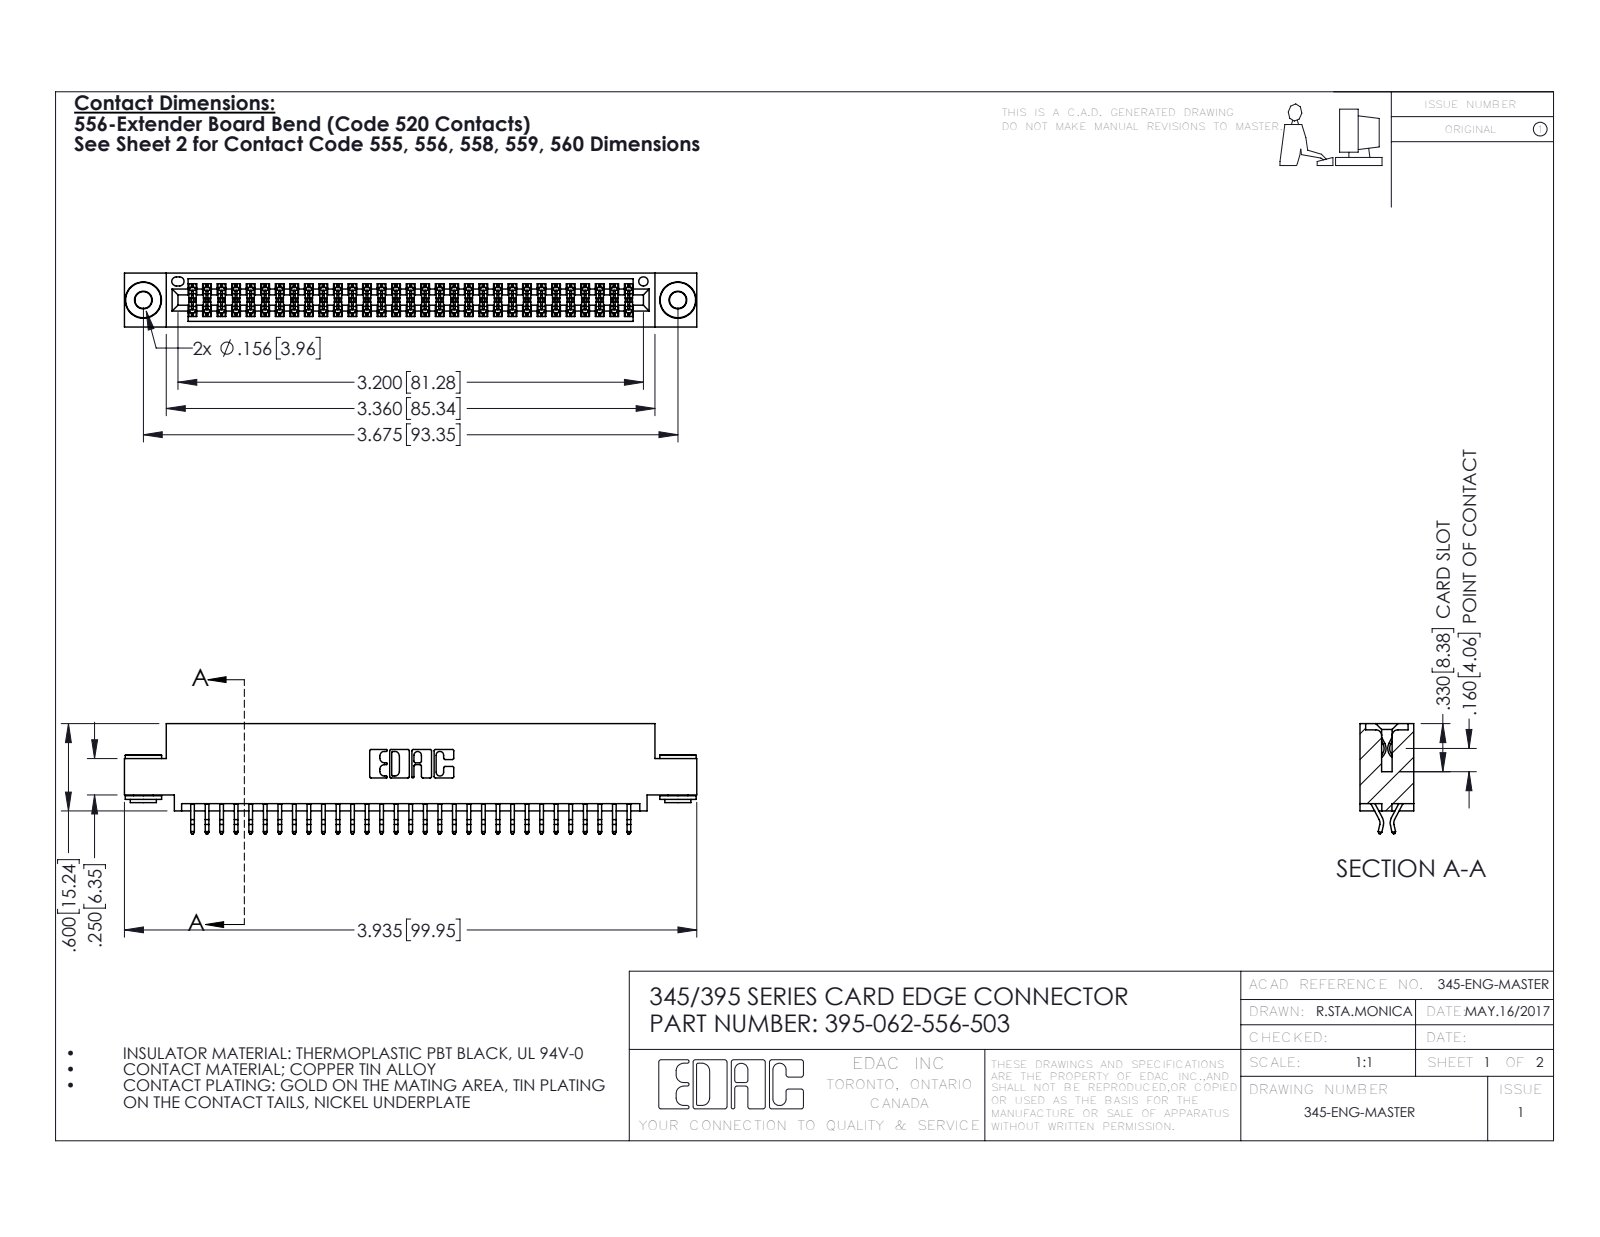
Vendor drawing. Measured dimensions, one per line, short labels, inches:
name: 395-062-556-503; 345-250-002_345-250-002-102; 345-292-001_556 Tail; 345 Part_0.110 Offset - 0.156 Dia-TH
written by: SolidWorks 2016 (CONFIG_CONTROL_DESIGN)
unit: in
bodies: 65 solids, 3640 faces (2388 planar, 1244 cylindrical, 8 other)
size: 3.935 × 0.757 × 0.37
volume: 0.583 in³; area: 21.93 in²
holes: 2× ⌀0.116, 2× ⌀0.156, 1× ⌀0.064
bosses: 2× ⌀0.25, 2× ⌀0.18, 2× ⌀0.136
rounds: 93× R0.006, 22× R0.01, 6× R0.007, 6× R0.031, 3× R0.026, 2× R0.01, 2× R0.014, 2× R0.019
face distances: 0.072, 0.298, 0.37, 0.2, 0.025, 0.098, 0.272, 0.225, 0.175, 0.149
hole spacings: 0.27, 3.44, 3.675
